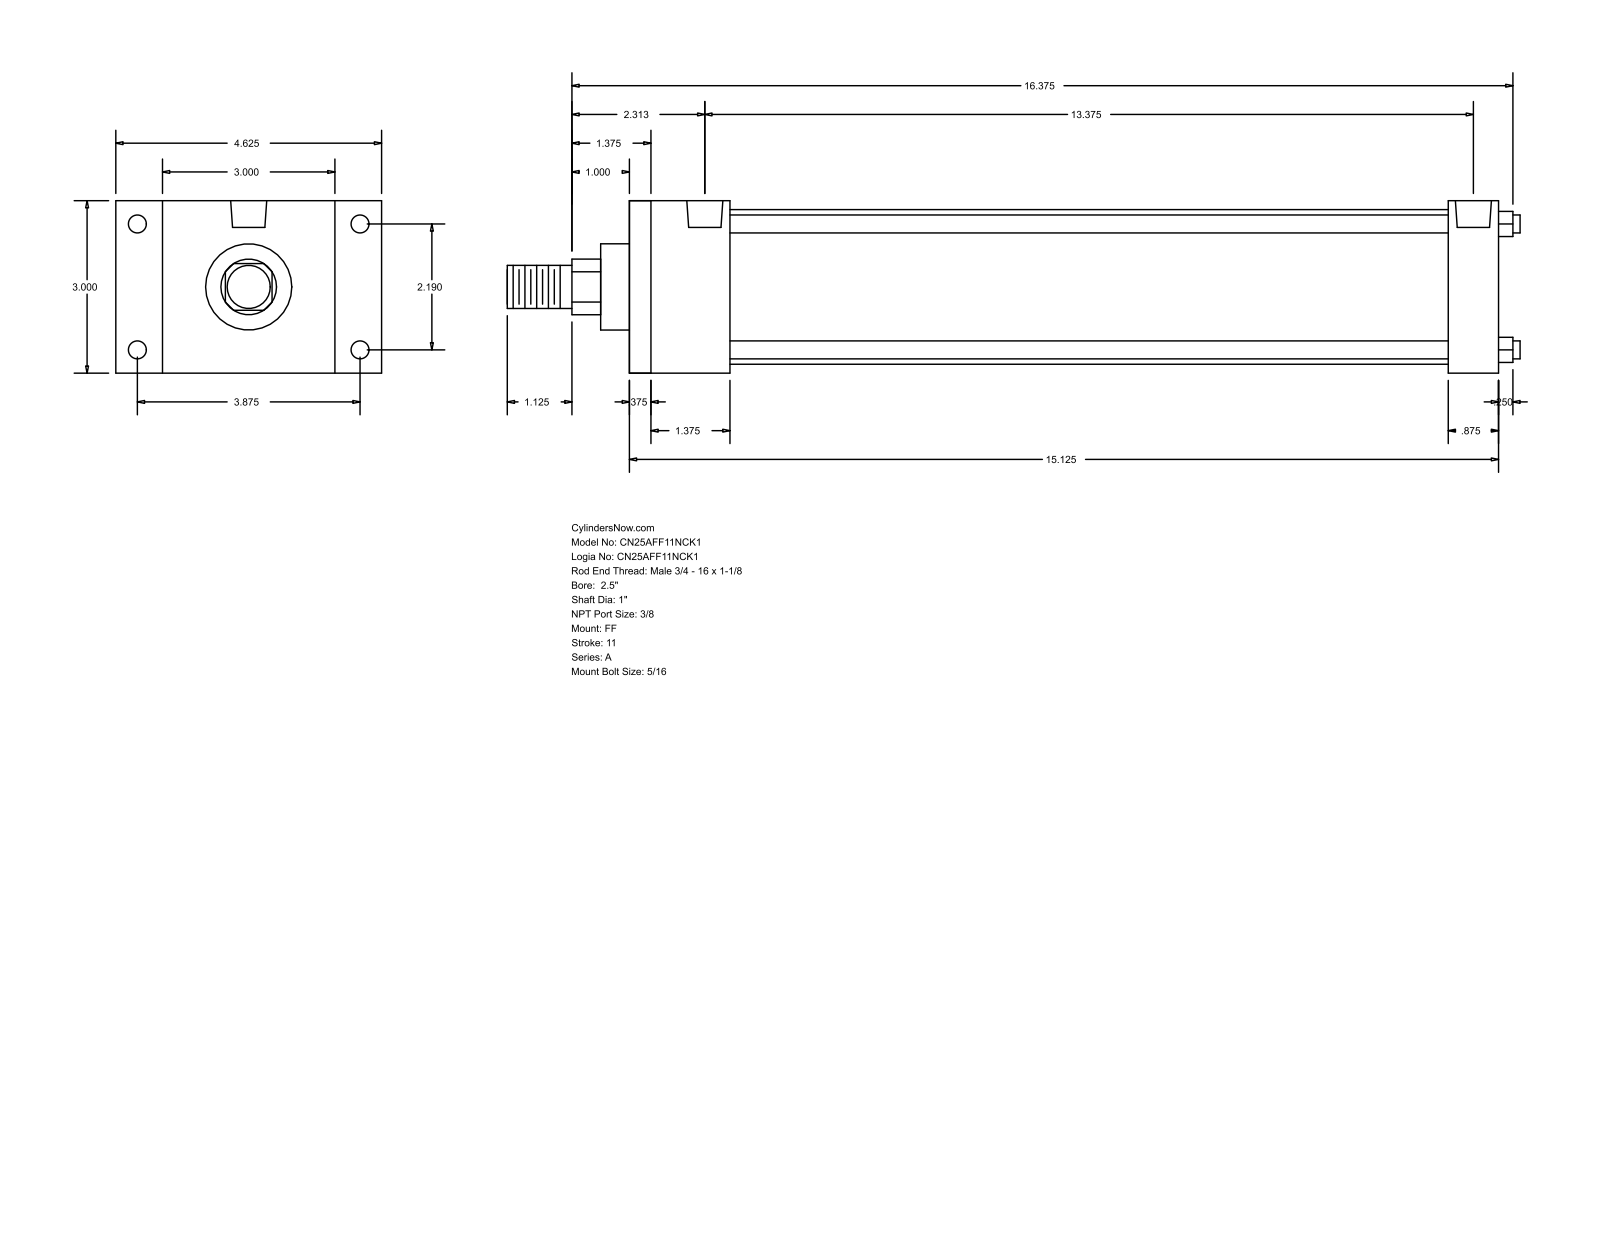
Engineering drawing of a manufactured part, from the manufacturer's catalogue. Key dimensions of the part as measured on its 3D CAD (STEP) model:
Part name (STEP PRODUCT): A_FF__0250_1
STEP written by: GSSL Pune (CONFIG_CONTROL_DESIGN)
Units: millimetres
Bodies: 0 solids, 92 faces (64 planar, 28 cylindrical, 0 other)
Overall size (bounding box): 447.68 × 117.47 × 76.2
Round holes (diameter × count): ⌀5.56 ×4, ⌀7.94 ×4, ⌀15.93 ×2
Round bosses / shafts (diameter × count): ⌀7.94 ×4, ⌀68.33 ×1, ⌀38.1 ×1, ⌀25.4 ×1, ⌀19.05 ×1
Partial cylindrical surfaces — rounded edges, fillets, slot ends (radius × count): R12.29 ×1
Main face-to-face distances: 76.2, 384.17, 374.65, 9.52, 22.22, 44.45, 361.95, 34.93, 352.43, 317.5
Hole centre spacings: 2.38, 55.62, 98.42, 113.05, 342.1, 344.48, 339.72
